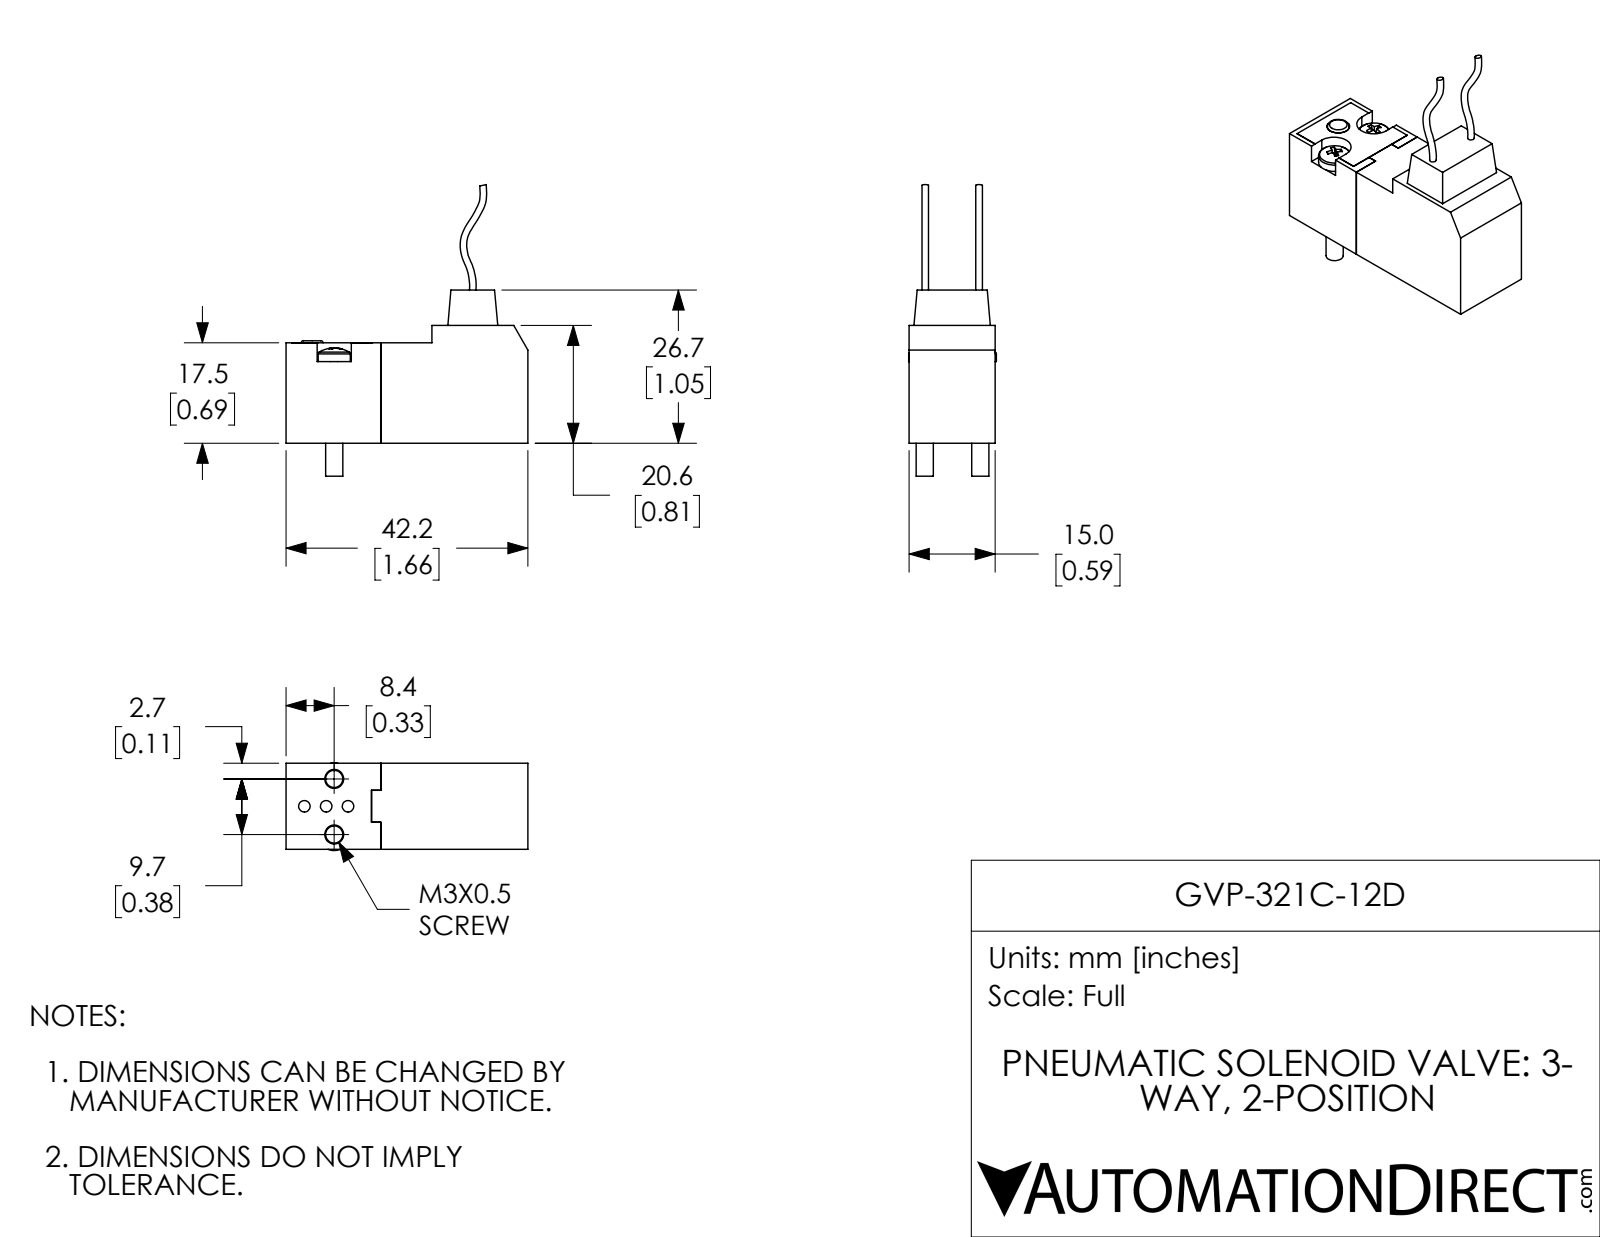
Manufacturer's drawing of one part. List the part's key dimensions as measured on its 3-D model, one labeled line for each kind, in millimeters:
Part name (STEP PRODUCT): GVP-321C-12D
STEP written by: SolidWorks 2018 (AUTOMOTIVE_DESIGN)
Units: millimetres
Bodies: 4 solids, 116 faces (79 planar, 23 cylindrical, 14 other)
Overall size (bounding box): 50.9 × 42.2 × 15.3
Volume: 12 400 mm³ · Surface area: 5 436 mm²
Round holes (diameter × count): ⌀2 ×3, ⌀3.3 ×2, ⌀3.9 ×1
Round bosses / shafts (diameter × count): ⌀5.6 ×2, ⌀3 ×2
Partial cylindrical surfaces — rounded edges, fillets, slot ends (radius × count): R3 ×2
Main face-to-face distances: 15, 16.5, 25.7, 42.2, 27.3, 1.6, 14.9, 17.5, 17.6, 4.7
Hole centre spacings: 3.8, 1.3, 2.5, 5, 5.1, 5.4, 5.5, 6.1
